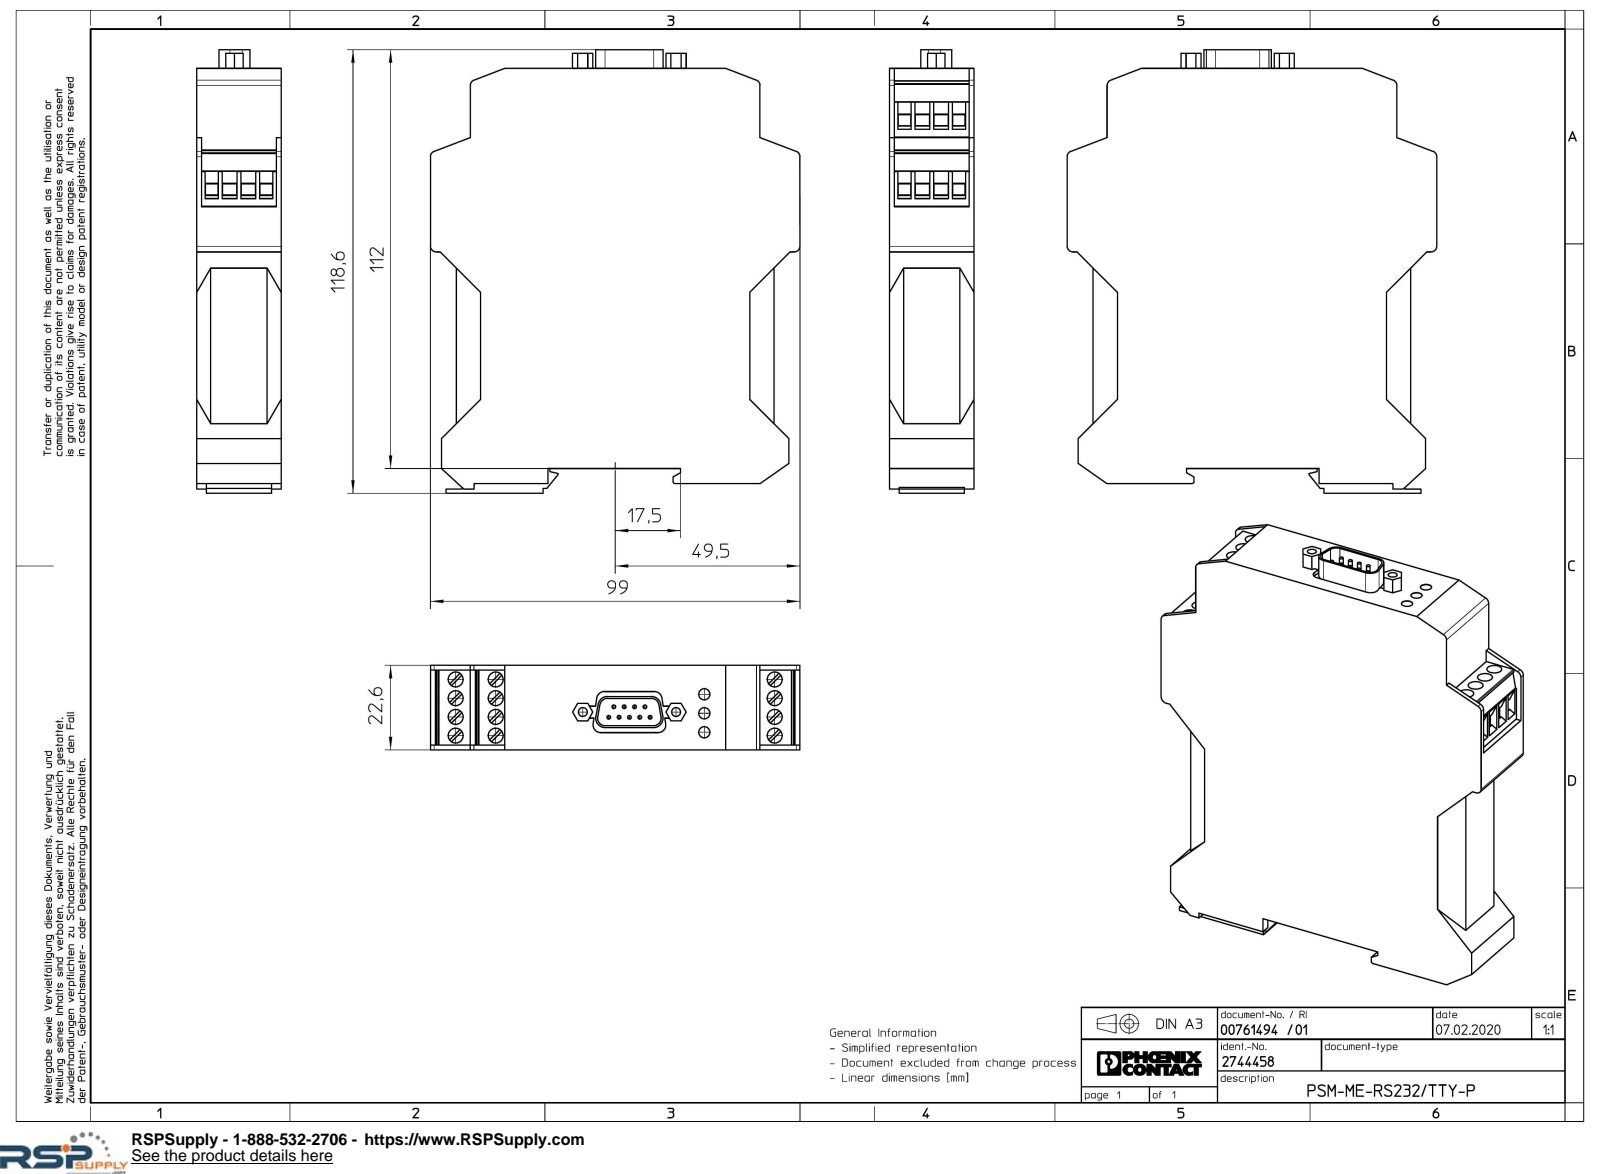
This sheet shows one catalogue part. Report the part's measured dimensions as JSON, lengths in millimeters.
{"part_name": "PSM_ME_RS232_..._P-select", "step_written_by": "Creo Elements/Direct Modeling 20.1A 29-Sep-2018 (C) Parametric Technology GmbH (AUTOMOTIVE_DESIGN)", "units": "millimeters", "bodies": {"solids": 1, "faces": 427, "planar": 347, "cylindrical": 80, "other": 0}, "overall_size": [118.6, 99, 22.6], "volume_mm3": 213149, "surface_area_mm2": 33258, "round_holes": [[4, 12], [3, 3], [2.4, 2]], "round_bosses_or_shafts": [[1, 9]], "partial_cylinders_radius": [[0.2, 6], [1.5, 6], [2, 4], [2.01, 4], [2.51, 4], [0.5, 1]], "face_to_face_distances": [22.6, 21.3, 1.3, 4, 107, 18.5, 85.1, 111, 6.95, 92.05], "hole_center_spacings": [5, 10, 11.81, 74.91, 85.59, 10.7, 14.65, 74.74]}
